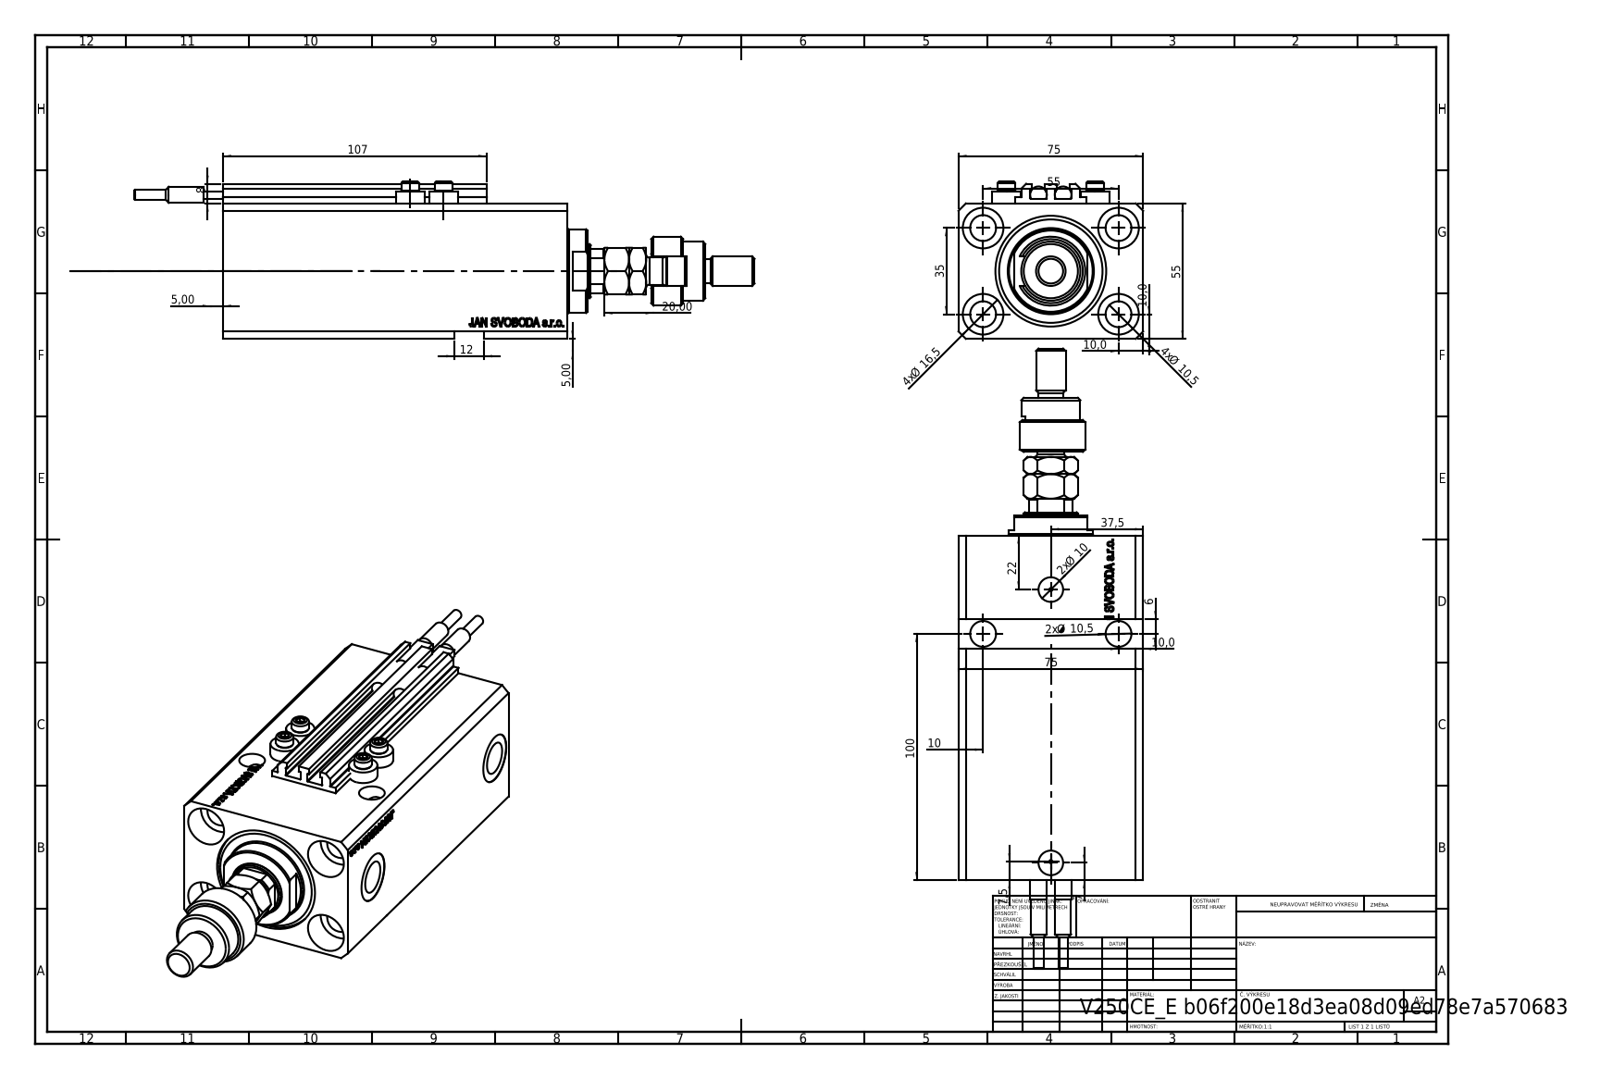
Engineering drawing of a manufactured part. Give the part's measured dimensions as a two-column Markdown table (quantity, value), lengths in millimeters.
| quantity | value |
| --- | --- |
| part name | SWITCH_V250CE; FEMALE_PART_FOR_DFA; ALLEN BOLT V250CE; V250CE_C_VCP (+3 more) |
| STEP written by | SolidWorks 2019 (CONFIG_CONTROL_DESIGN) |
| units | millimeters |
| bodies | 12 solids, 1201 faces (574 planar, 151 cylindrical, 476 other) |
| overall size | 251.9 × 75 × 64 |
| volume | 513 088 mm³ |
| surface area | 126 259 mm² |
| round holes (diameter × count) | 10.5 × 7, 1.25 × 4, 4 × 4, 16.5 × 4, 10 × 2, 13.16 × 2, 20 × 2, 22 × 1, 32 × 1, 45 × 1 |
| round bosses / shafts (diameter × count) | 11.6 × 4, 7 × 4, 6.8 × 2, 6.5 × 2, 4 × 2, 34 × 1, 28 × 1, 24 × 1 |
| partial cylindrical surfaces (radius × count) | 0.2 × 10, 9.75 × 1, 10.5 × 1 |
| main face-to-face distances | 55, 75, 3, 57, 27.1, 140, 8, 112.9, 9.9, 2 |
| hole center spacings | 32.6, 55, 13.6, 14.09, 25.81, 32.87, 33.62, 35 |
